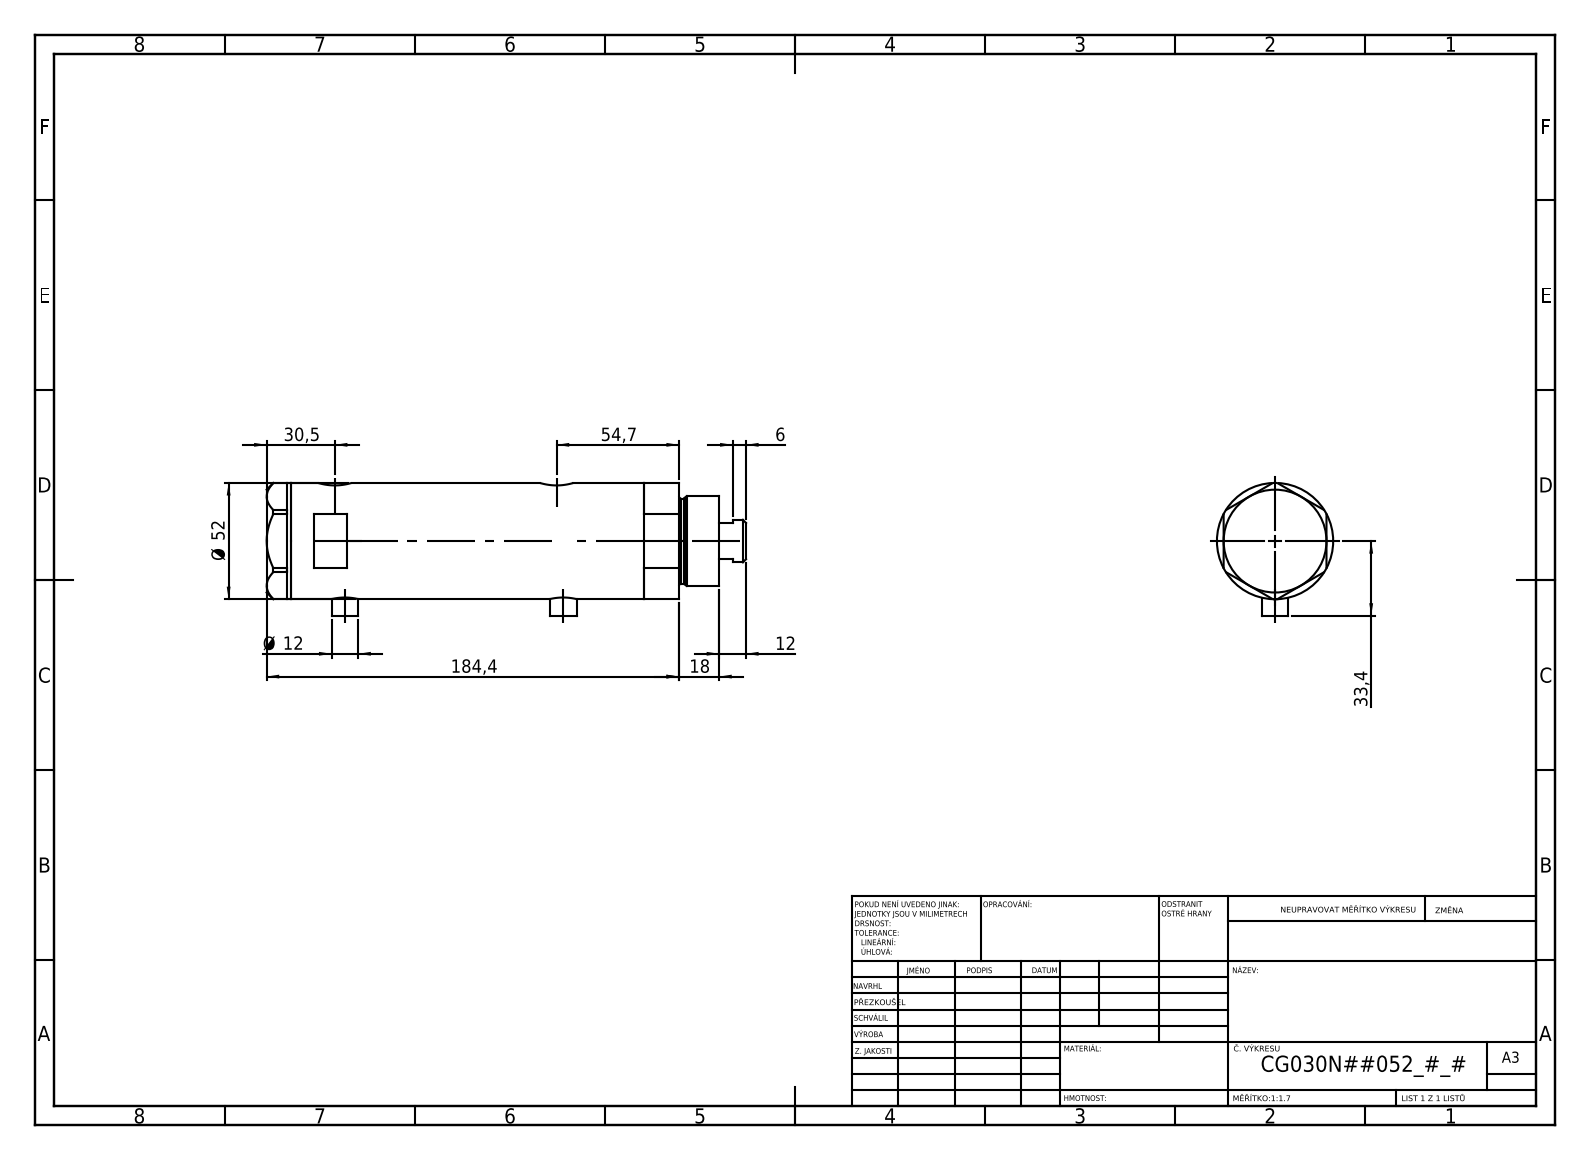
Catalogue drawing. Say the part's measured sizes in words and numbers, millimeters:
The part is named "V270CG_FRONT; V270CG_BACK; V270CG_MIDDLE; V270CG_VC". Its 3-D file was written by "SolidWorks 2019 (CONFIG_CONTROL_DESIGN)". It is 4 solids with 134 faces: 65 planar, 49 cylindrical and 20 other. Overall it measures 214.4 by 59.4 by 52 millimeters. Its volume is 389 992 cubic millimeters and its surface area 86 999 square millimeters. Round holes: 2 of diameter 9.73, 2 of diameter 12.5, 2 of diameter 15, 1 of diameter 6.5, 1 of diameter 20, 1 of diameter 21.5, 1 of diameter 30, 1 of diameter 33, 1 of diameter 44. Round bosses or shafts: 2 of diameter 12, 1 of diameter 52, 1 of diameter 40, 1 of diameter 38, 1 of diameter 19. The main face-to-face distances are 121.5, 23.8, 97.7, 11, 34.8, 132.5, 46, 168.9, 157.9, 134.1. The hole center spacings are 2.9, 4.5, 94.7, 97.6, 99.2, 102.1.
